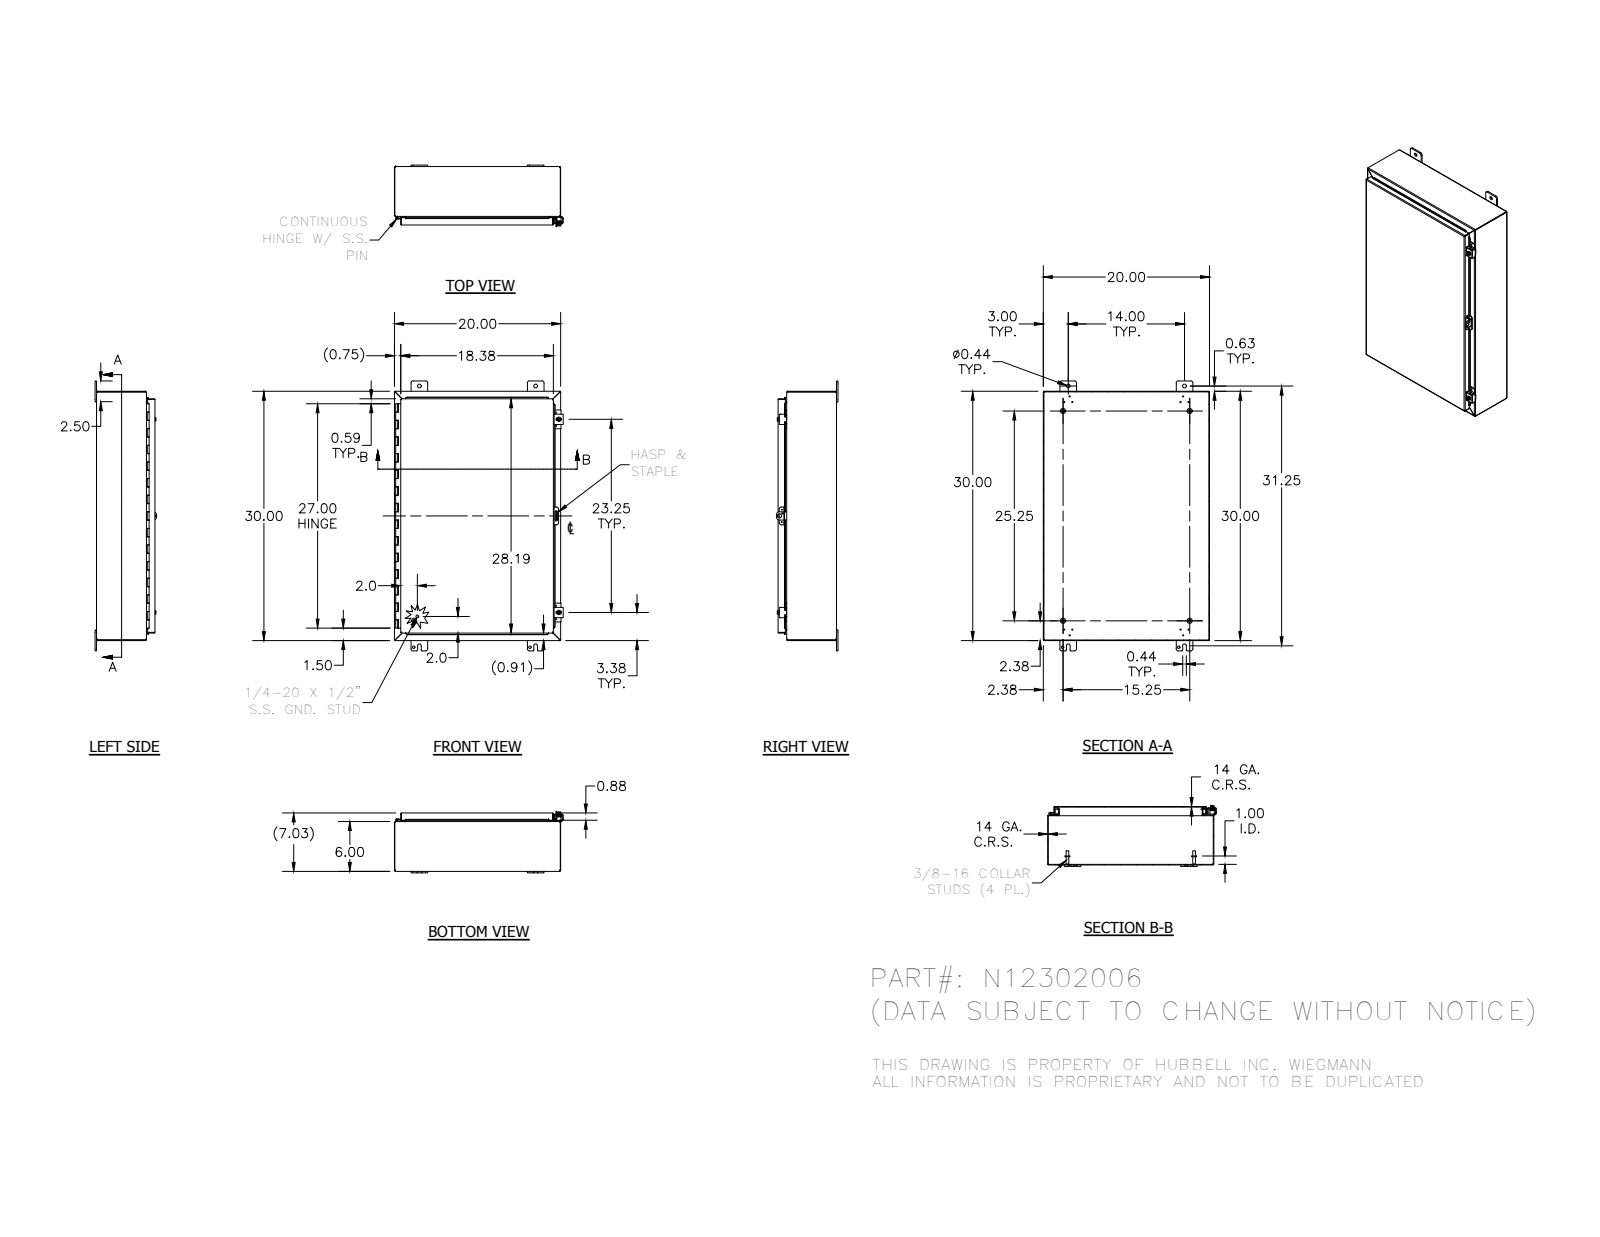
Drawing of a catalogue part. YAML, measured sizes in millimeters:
part_name: "N12302006; 34840; 38420; N12302006BKP (+8 more)"
step_written_by: "Autodesk Inventor 2012 (AUTOMOTIVE_DESIGN)"
units: millimeters
bodies: {solids: 27, faces: 1033, planar: 566, cylindrical: 350, other: 117}
overall_size: [825.5, 515.9, 188.2]
volume: 2730000
surface_area: 2805000
round_holes:
  - {diameter: 3, count: 12}
  - {diameter: 2.8, count: 7}
  - {diameter: 8, count: 4}
  - {diameter: 11.1, count: 4}
  - {diameter: 5.4, count: 2}
  - {diameter: 7.1, count: 2}
  - {diameter: 7.6, count: 2}
  - {diameter: 3.2, count: 1}
  - {diameter: 4, count: 1}
  - {diameter: 12.7, count: 1}
round_bosses_or_shafts:
  - {diameter: 15.9, count: 4}
  - {diameter: 8.4, count: 4}
  - {diameter: 6.4, count: 4}
  - {diameter: 13.2, count: 2}
  - {diameter: 12.7, count: 2}
  - {diameter: 8.9, count: 2}
  - {diameter: 2.9, count: 2}
  - {diameter: 8.6, count: 1}
partial_cylinders:
  - {radius: 0.8, count: 27}
  - {radius: 1.6, count: 25}
  - {radius: 3.2, count: 25}
  - {radius: 6.4, count: 25}
  - {radius: 0.8, count: 23}
  - {radius: 2.7, count: 23}
  - {radius: 1.8, count: 8}
  - {radius: 2.5, count: 4}
face_to_face_distances: [1.9, 176.8, 174.9, 178.6, 506.1, 150.5, 26.2, 760.1, 504.2, 508]
hole_center_spacings: [355.6, 19.3, 23.9, 24.6, 50.7, 339.7, 364.3, 695.5]
